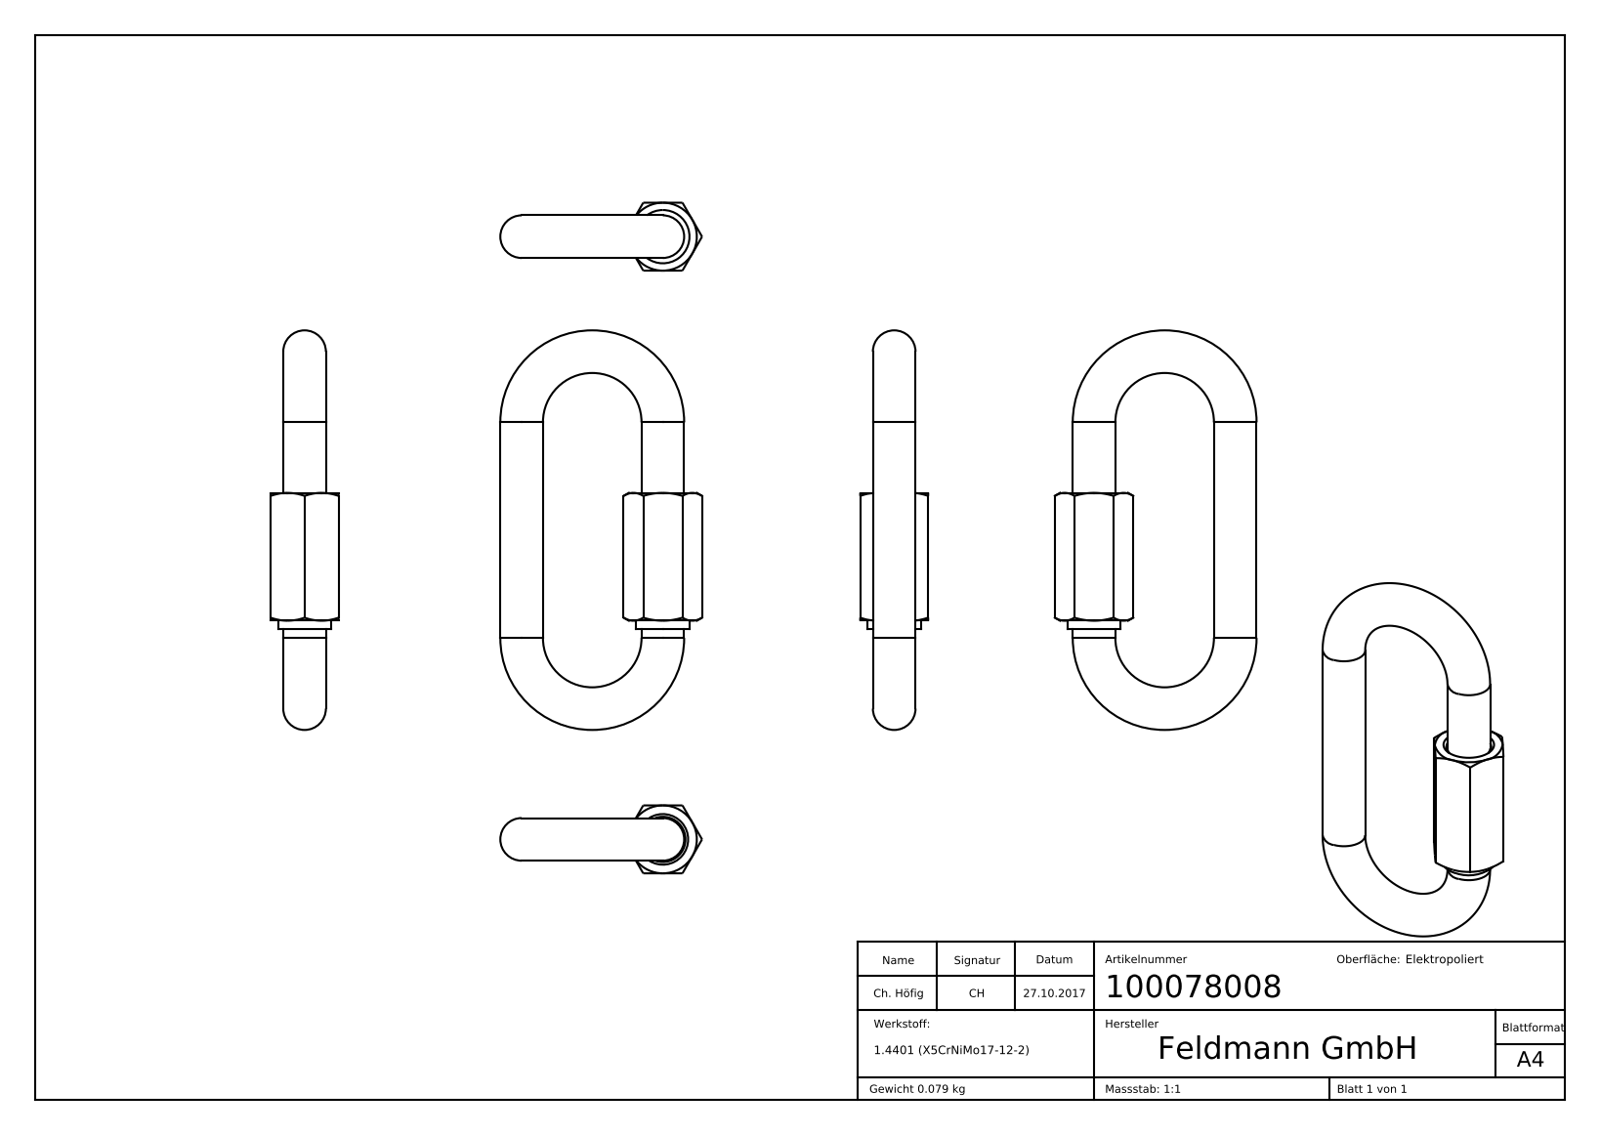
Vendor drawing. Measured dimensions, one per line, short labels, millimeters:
name: 10007800X Teil2_100078008 Teil2; 100078008; 10007800X Teil1_100078008 Teil1
written by: SolidWorks 2015 (CONFIG_CONTROL_DESIGN)
unit: mm
bodies: 2 solids, 60 faces (12 planar, 18 cylindrical, 30 other)
size: 75 × 37.86 × 12.75
volume: 9 884 mm³; area: 5 884 mm²
holes: 1× ⌀8.5
bosses: 2× ⌀8, 1× ⌀10, 1× ⌀9, 1× ⌀8.6
face distances: 12.75, 12.74, 24, 6.5, 17.3, 10.8, 17.5, 6.7, 1.5, 8
